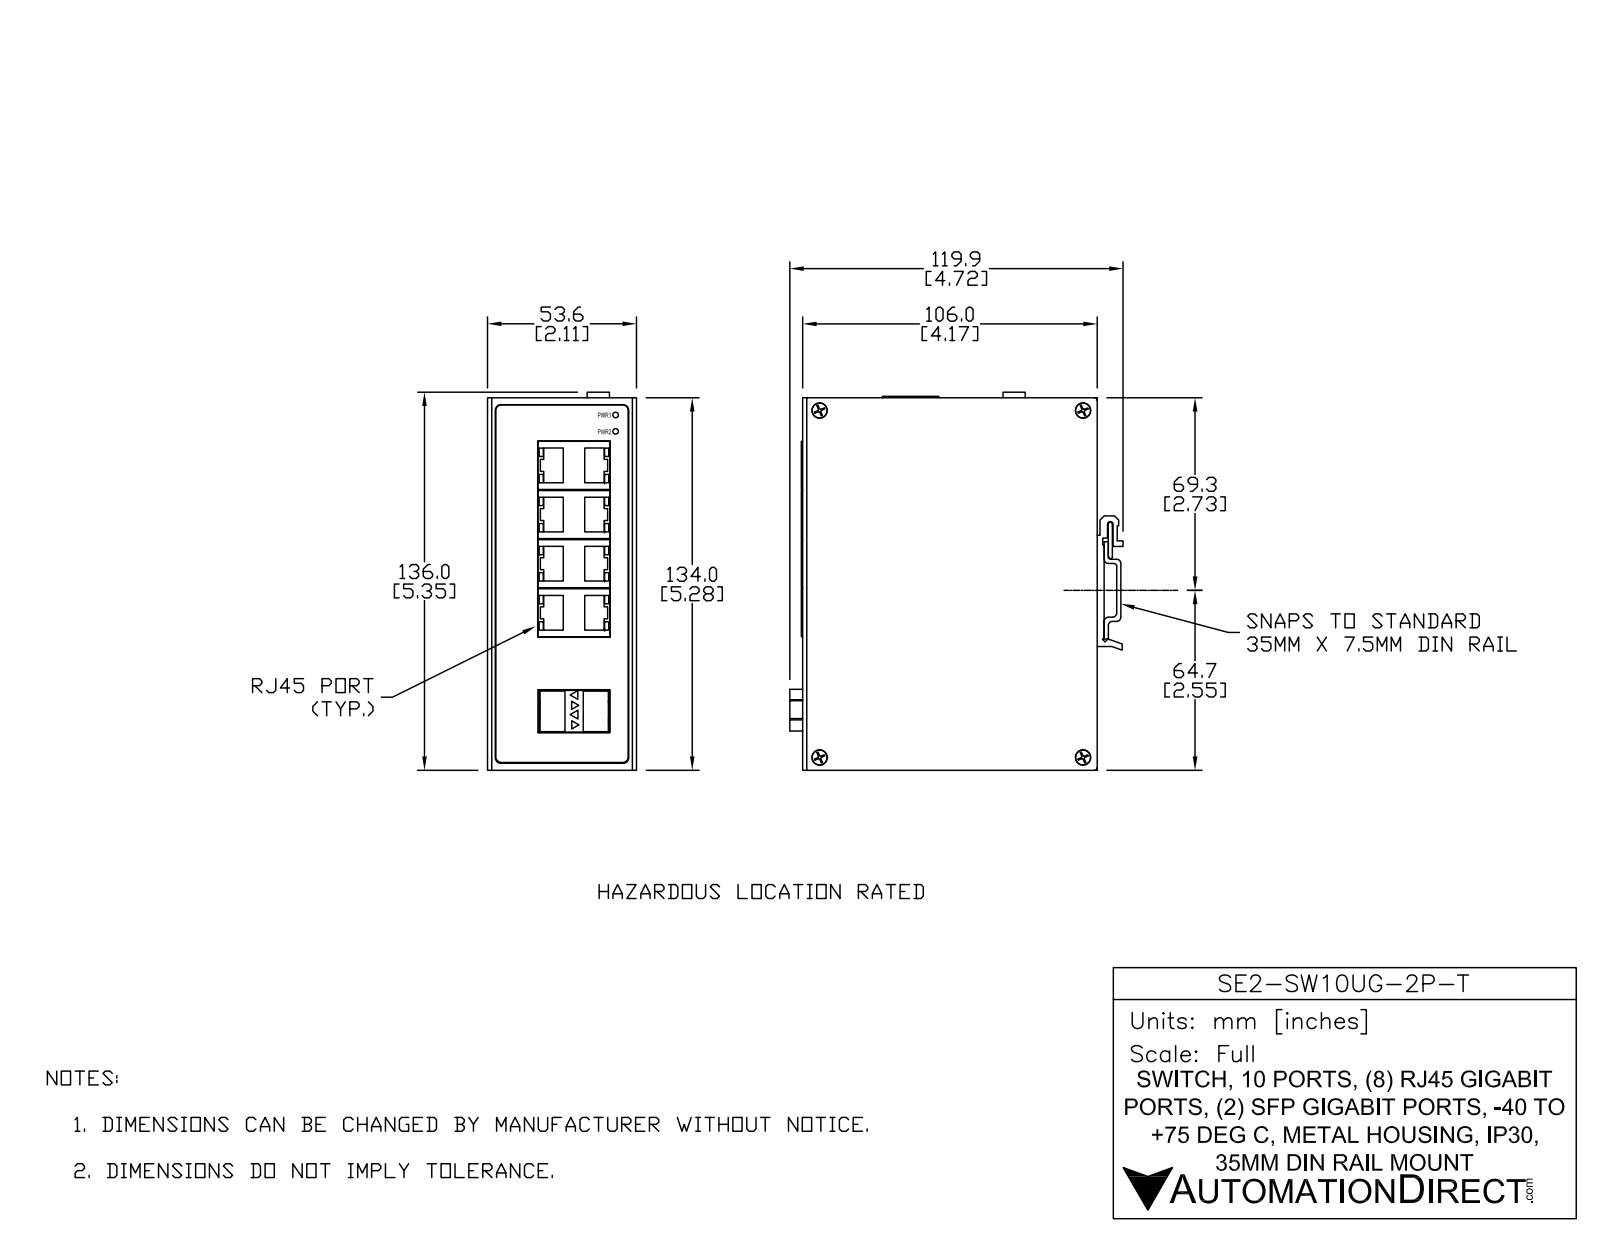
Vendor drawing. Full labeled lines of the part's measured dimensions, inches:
Part name (STEP PRODUCT): SE2-SW10UG-2P-T
STEP written by: SolidWorks 2017 (AUTOMOTIVE_DESIGN)
Units: inches
Bodies: 32 solids, 1643 faces (1159 planar, 350 cylindrical, 134 other)
Overall size (bounding box): 5.728 × 4.949 × 2.11
Volume: 7.904 in³ · Surface area: 274.6 in²
Round holes (diameter × count): ⌀0.098 ×9, ⌀0.12 ×6, ⌀0.051 ×4, ⌀0.11 ×4, ⌀0.15 ×4, ⌀0.118 ×2, ⌀0.138 ×2, ⌀0.079 ×1
Round bosses / shafts (diameter × count): ⌀0.248 ×9, ⌀0.138 ×7, ⌀0.059 ×6, ⌀0.142 ×4, ⌀0.118 ×4, ⌀0.051 ×4, ⌀0.024 ×4, ⌀0.315 ×1
Partial cylindrical surfaces — rounded edges, fillets, slot ends (radius × count): R0.023 ×86, R0.01 ×22, R0.015 ×14, R0.041 ×6, R0.039 ×5, R0.012 ×4, R0.02 ×4, R0.03 ×4
Main face-to-face distances: 0.039, 2.031, 2.071, 0.079, 1.992, 2.11, 5.236, 4.114, 5.276, 5.197
Hole centre spacings: 0.544, 0.2, 5.938, 0.203, 0.4, 0.4, 0.582, 0.63
